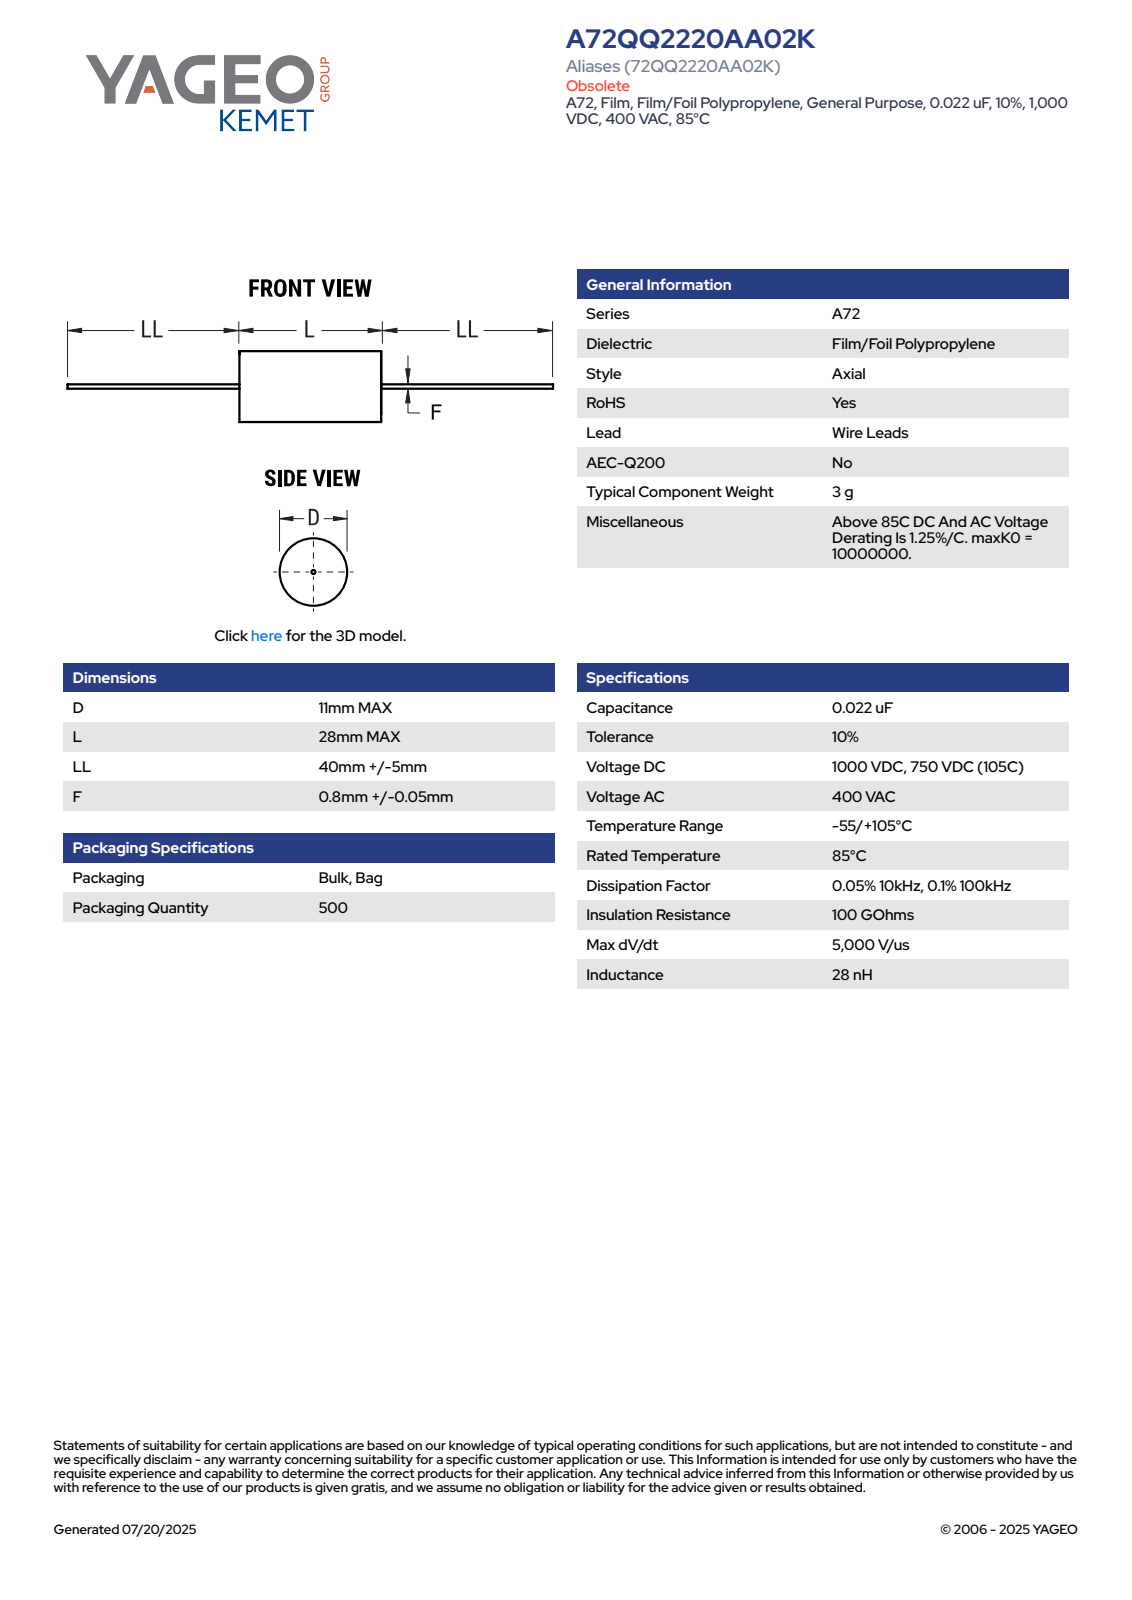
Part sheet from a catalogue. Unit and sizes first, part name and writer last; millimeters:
Units: millimetres
Overall size (bounding box): 118 × 11.01 × 11
Round bosses / shafts (diameter × count): ⌀11 ×1, ⌀0.85 ×1
Partial cylindrical surfaces — rounded edges, fillets, slot ends (radius × count): R5.51 ×1
Main face-to-face distances: 28, 45, 73, 118
Volume: 2 712 mm³ · Surface area: 1 399 mm²
Bodies: 1 solid, 72 faces (26 planar, 15 cylindrical, 31 other)
Part name (STEP PRODUCT): CFA_ACWF_11X28_D11L28LL45F0.85
STEP written by: SolidWorks 2014 (AUTOMOTIVE_DESIGN)
